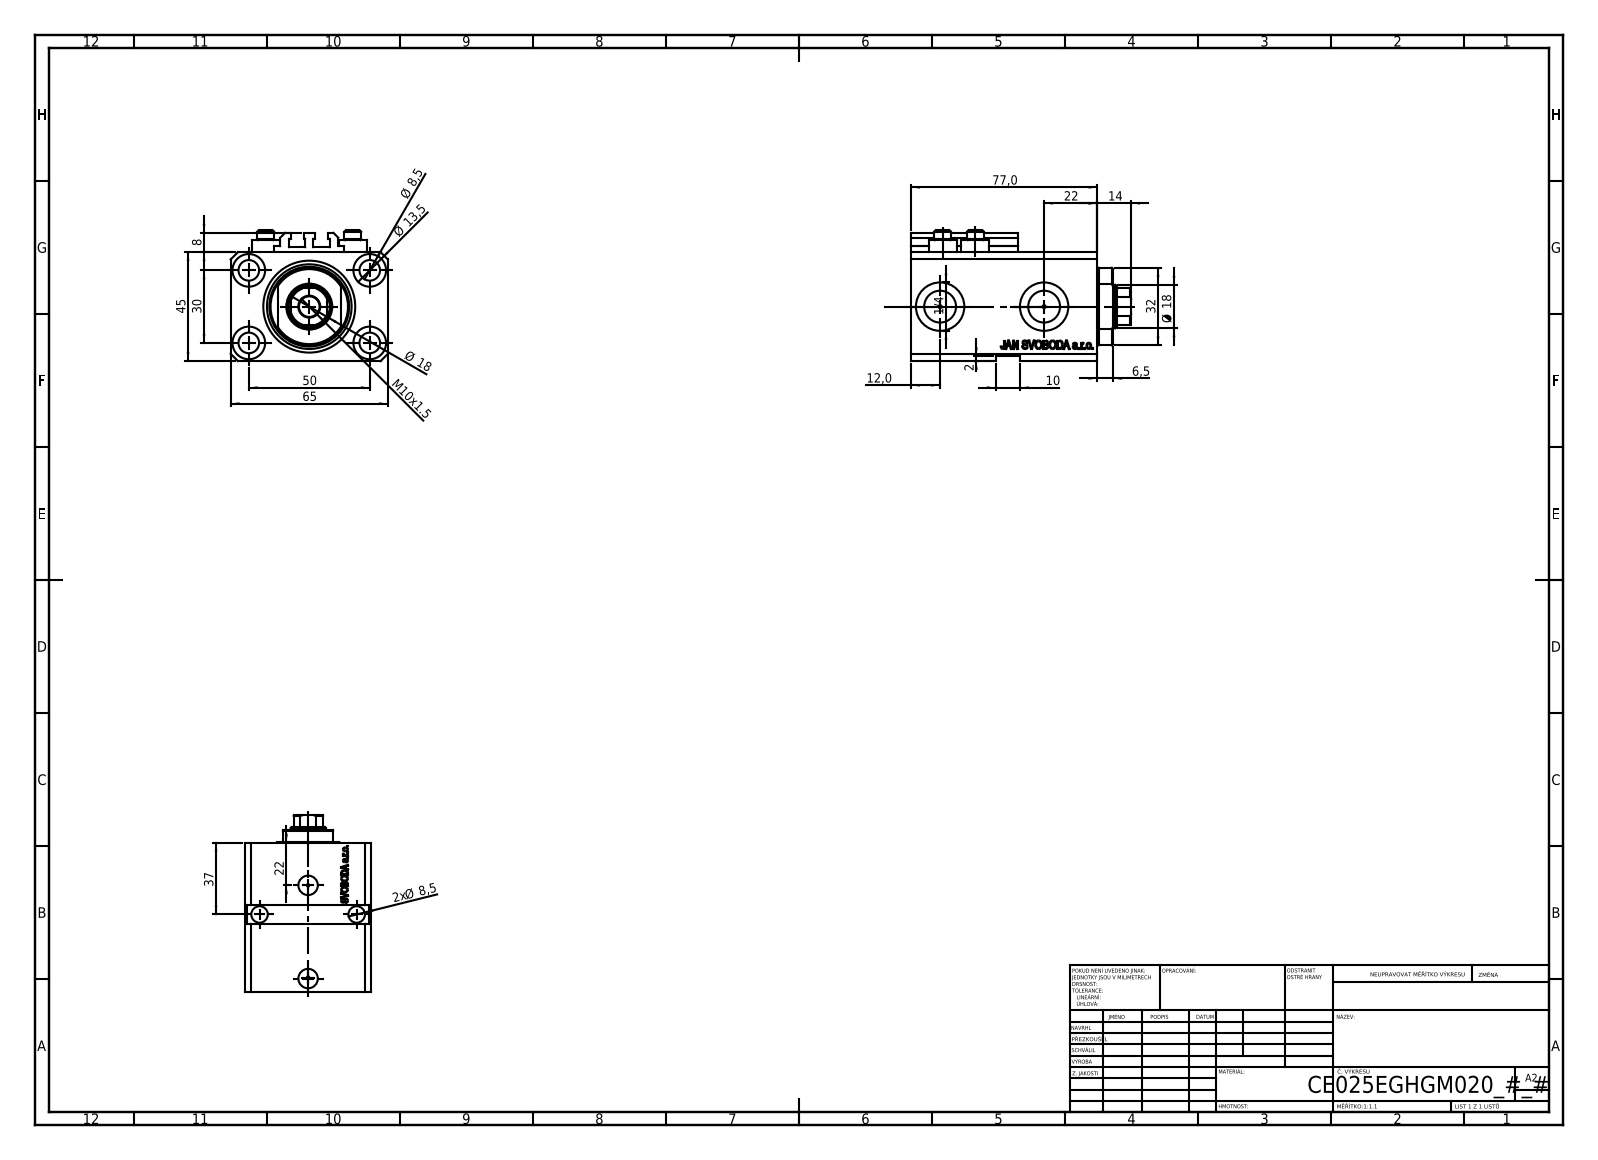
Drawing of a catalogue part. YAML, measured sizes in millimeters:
part_name: "V250CE_VC_E; V250CE_C_VCP; ALLEN BOLT V250CE; V250CE_E_Body"
step_written_by: "SolidWorks 2019 (CONFIG_CONTROL_DESIGN)"
units: millimeters
bodies: {solids: 8, faces: 1067, planar: 511, cylindrical: 126, other: 430}
overall_size: [91, 65, 54]
volume: 199775
surface_area: 59185
round_holes:
  - {diameter: 8.5, count: 7}
  - {diameter: 1.25, count: 4}
  - {diameter: 4, count: 4}
  - {diameter: 13.5, count: 4}
  - {diameter: 10, count: 2}
  - {diameter: 13.16, count: 2}
  - {diameter: 20, count: 2}
  - {diameter: 18, count: 1}
  - {diameter: 25, count: 1}
  - {diameter: 38, count: 1}
round_bosses_or_shafts:
  - {diameter: 11.6, count: 4}
  - {diameter: 7, count: 4}
partial_cylinders:
  - {radius: 0.2, count: 10}
  - {radius: 8.5, count: 1}
  - {radius: 16, count: 1}
face_to_face_distances: [45, 65, 63, 14, 77, 2, 6.9, 56.1, 70.1, 47]
hole_center_spacings: [29.15, 50, 13.6, 15.12, 18.81, 18.97, 26.22, 26.61]
